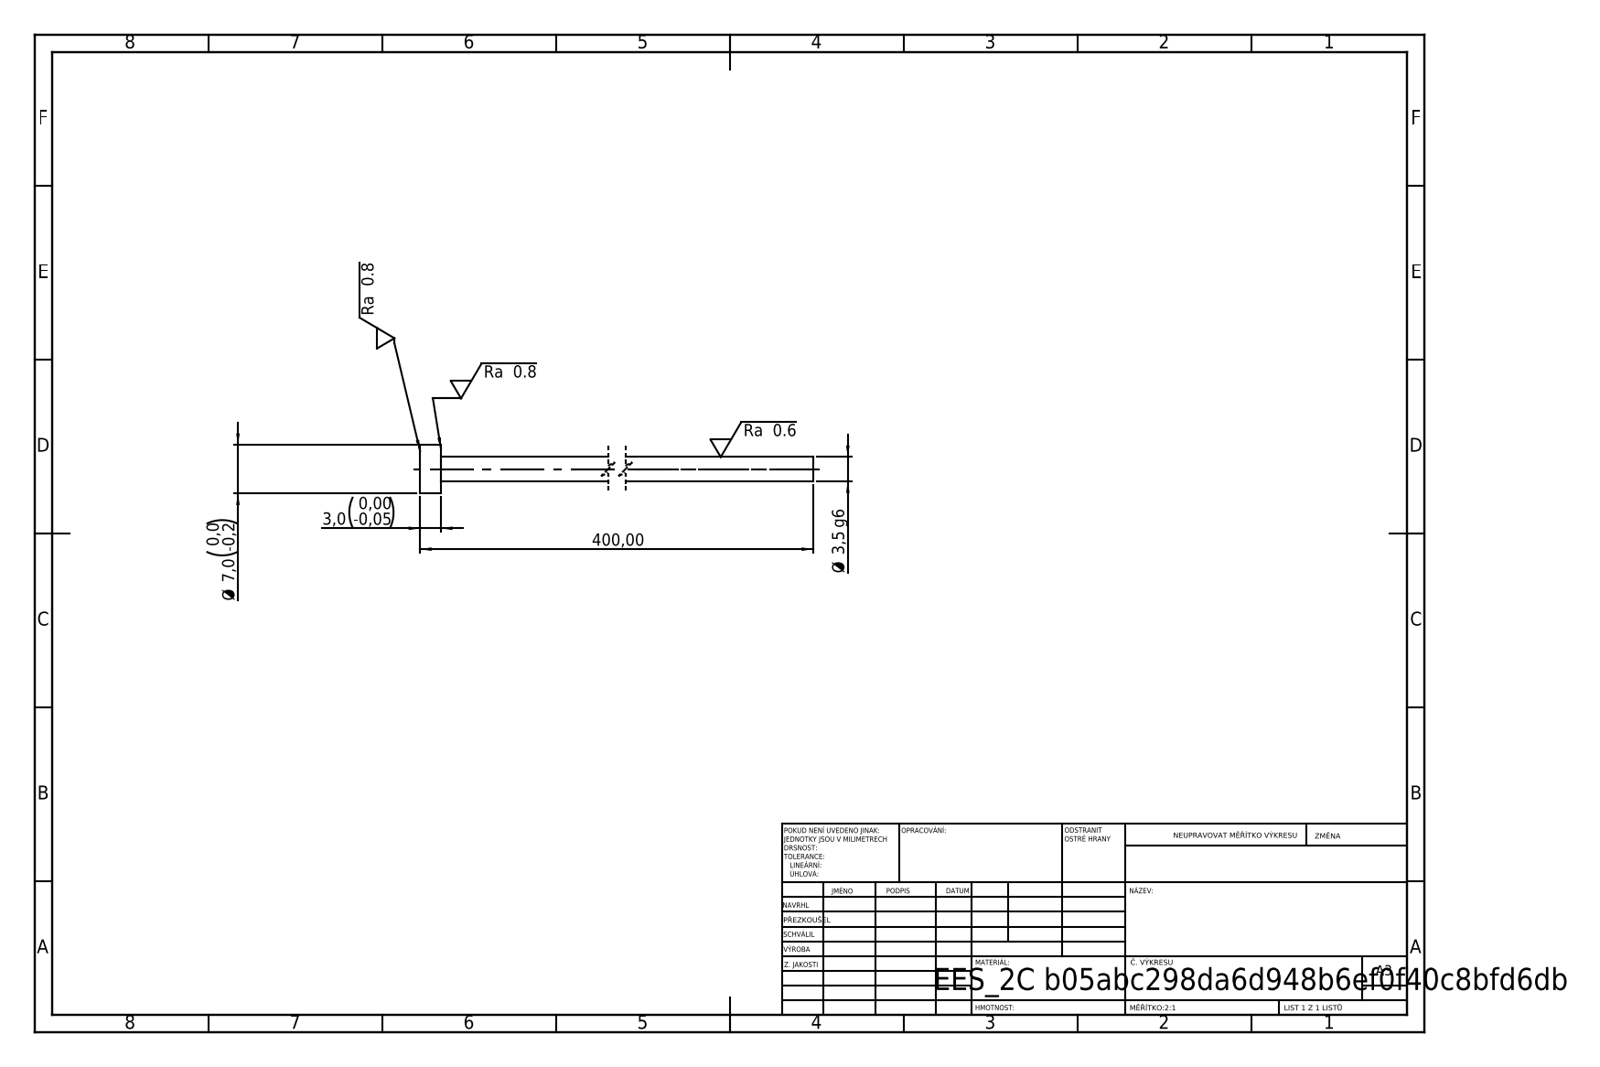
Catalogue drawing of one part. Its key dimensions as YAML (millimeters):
step_written_by: "SolidWorks 2019 (CONFIG_CONTROL_DESIGN)"
units: millimeters
bodies: {solids: 1, faces: 7, planar: 3, cylindrical: 4, other: 0}
overall_size: [400, 7, 7]
volume: 3935
surface_area: 4508
round_bosses_or_shafts:
  - {diameter: 7, count: 1}
  - {diameter: 3.5, count: 1}
face_to_face_distances: [3, 400, 397]
